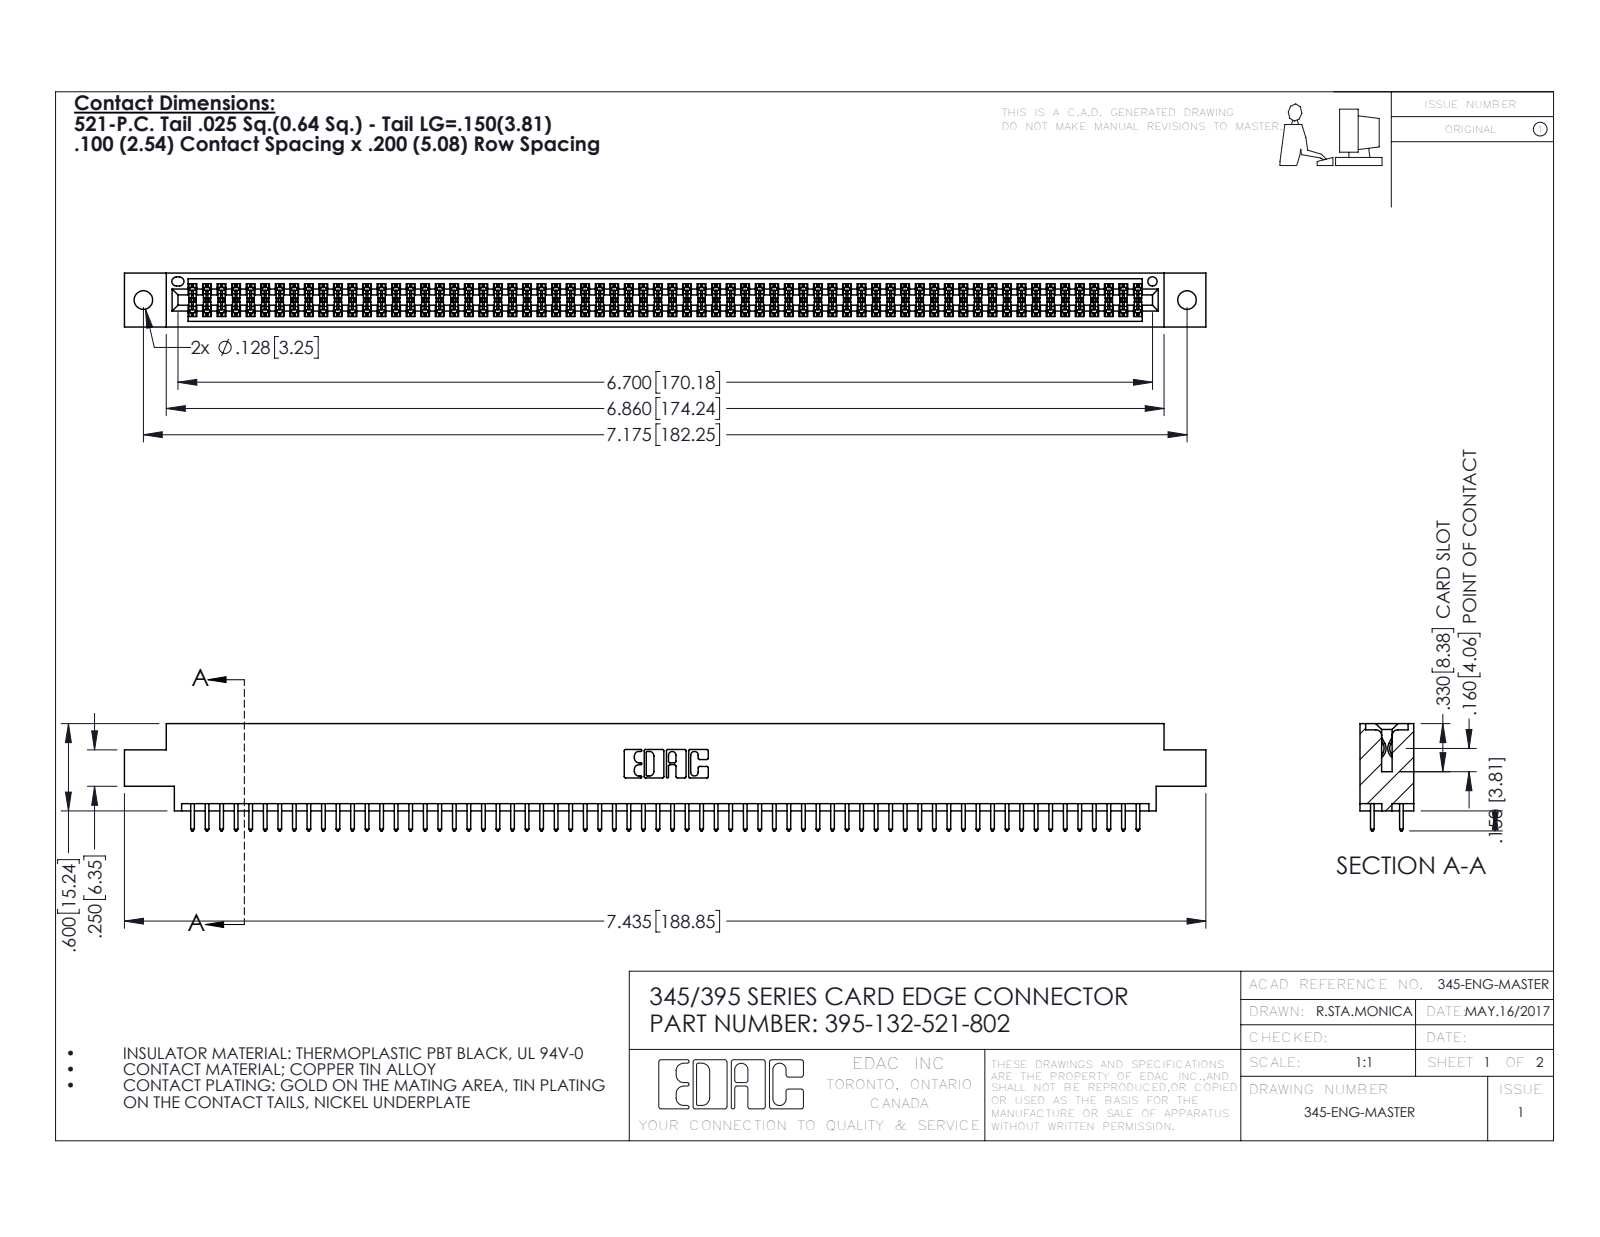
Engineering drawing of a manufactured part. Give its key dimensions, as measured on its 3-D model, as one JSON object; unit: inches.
{"part_name": "345 Part_0.170 Offset - 0.128 Dia; 345-292-001_345-293-121; 395-132-521-802", "step_written_by": "SolidWorks 2016 (CONFIG_CONTROL_DESIGN)", "units": "inches", "bodies": {"solids": 133, "faces": 6730, "planar": 4440, "cylindrical": 2290, "other": 0}, "overall_size": [7.435, 0.737, 0.37], "volume_in3": 1.121, "surface_area_in2": 42.05, "round_holes": [[0.128, 2], [0.064, 1]], "partial_cylinders_radius": [[0.006, 198], [0.01, 132], [0.01, 22], [0.007, 6], [0.031, 6], [0.026, 3], [0.014, 2], [0.019, 2]], "face_to_face_distances": [0.072, 0.298, 0.2, 0.37, 0.098, 0.272, 0.025, 0.225, 0.175, 0.149], "hole_center_spacings": [0.27, 6.939, 7.175]}
